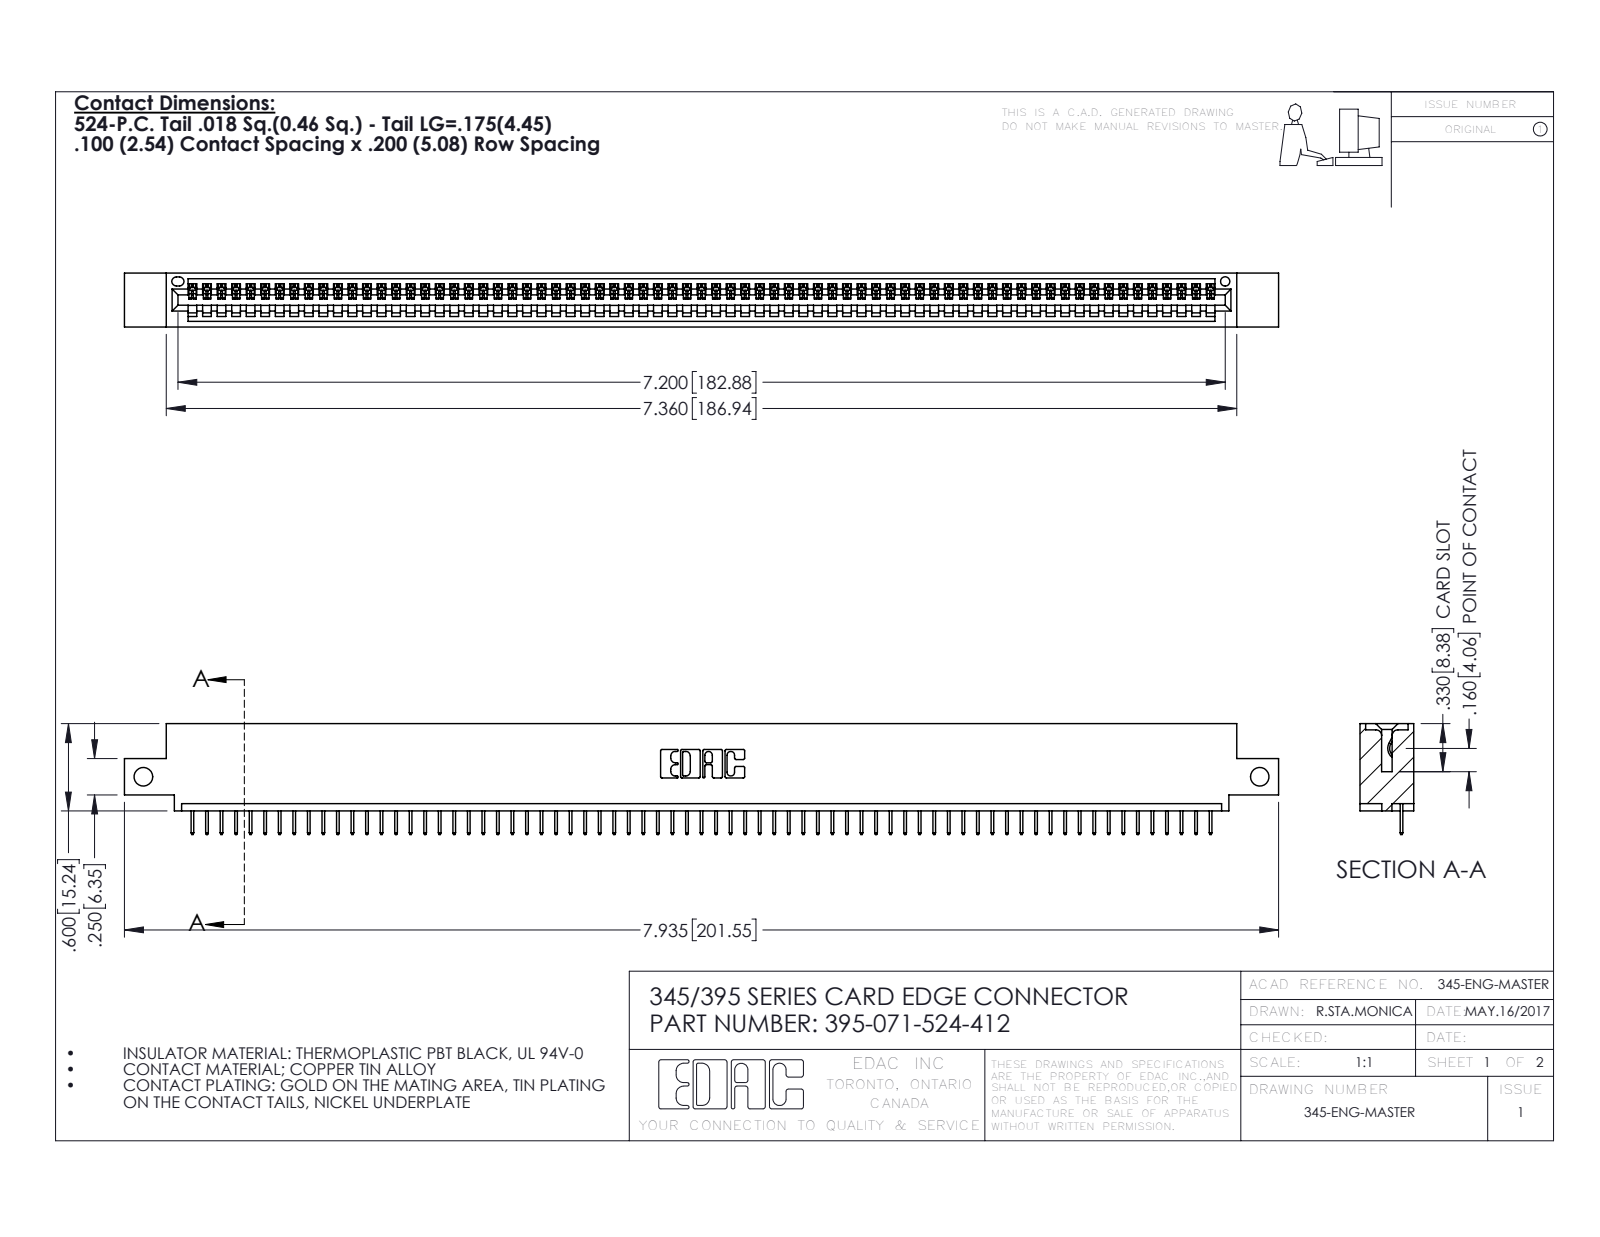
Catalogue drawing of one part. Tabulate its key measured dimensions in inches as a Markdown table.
| quantity | value |
| --- | --- |
| part name | 395-071-524-412; 345 Part_0.110 Offset - Side Mount; 345-292-001_345-293-124 |
| STEP written by | SolidWorks 2016 (CONFIG_CONTROL_DESIGN) |
| units | inches |
| bodies | 72 solids, 4532 faces (3350 planar, 1182 cylindrical, 0 other) |
| overall size | 7.935 × 0.762 × 0.37 |
| volume | 1.156 in³ |
| surface area | 38.14 in² |
| round holes (diameter × count) | 0.128 × 2, 0.064 × 1 |
| partial cylindrical surfaces (radius × count) | 0.006 × 142, 0.01 × 22, 0.007 × 6, 0.031 × 6, 0.026 × 3, 0.031 × 2, 0.04 × 2, 0.014 × 1 |
| main face-to-face distances | 0.072, 0.298, 0.37, 0.2, 0.098, 0.272, 0.025, 0.225, 0.072, 0.149 |
| hole center spacings | 7.675 |
